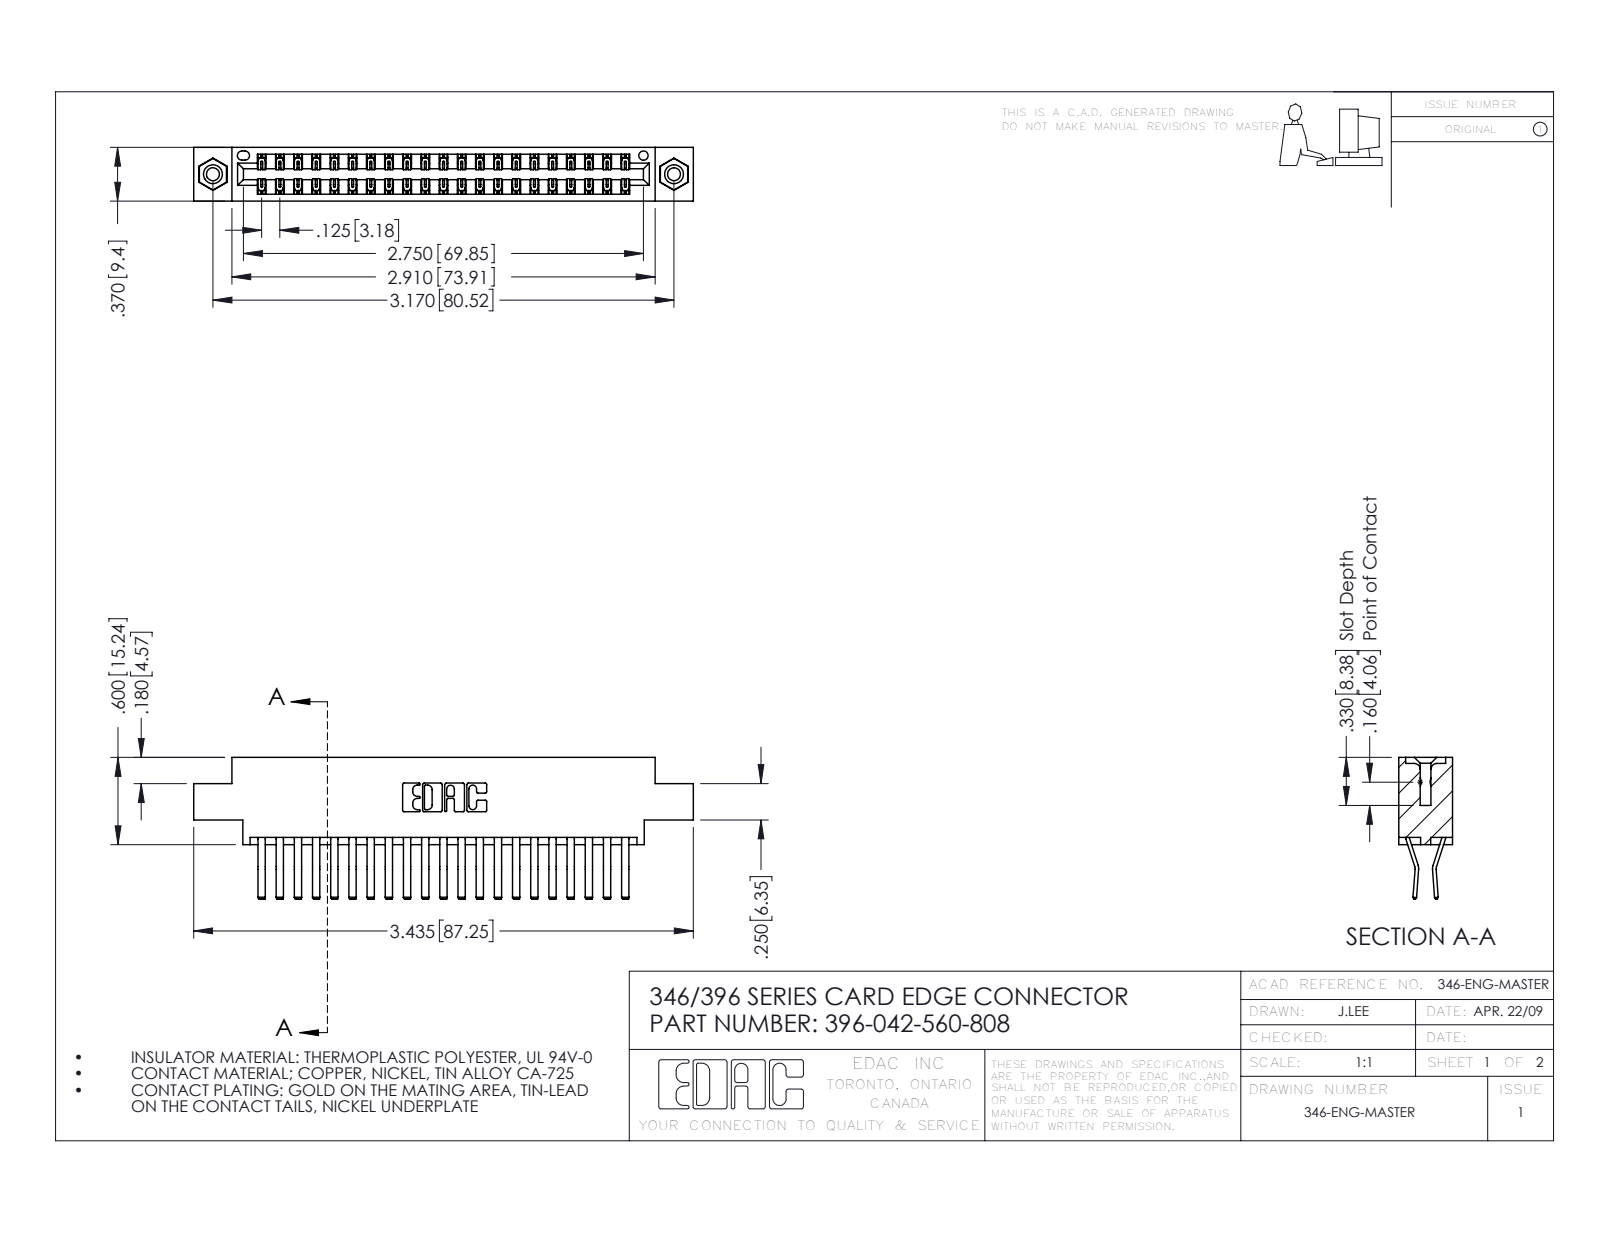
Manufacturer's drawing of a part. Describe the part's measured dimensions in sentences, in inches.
The part is named "346 Part_0.170 Offset - 0.156 Dia-TI; 345-250-001_345-250-003-102; 396-042-560-808; 345-292-001_560 Tail". Its 3-D file was written by "SolidWorks 2016 (CONFIG_CONTROL_DESIGN)". It is 45 solids with 2454 faces: 1582 planar, 856 cylindrical and 16 other. Overall it measures 3.435 by 0.975 by 0.37 inches. Its volume is 0.516 cubic inches and its surface area 18.96 square inches. Round holes: 2 of diameter 0.089, 2 of diameter 0.125, 2 of diameter 0.156, 1 of diameter 0.064. Round bosses or shafts: 2 of diameter 0.155. Partial cylindrical surfaces (rounded edges, fillets, slot ends): 63 of radius 0.006, 22 of radius 0.01, 6 of radius 0.007, 6 of radius 0.031, 3 of radius 0.026, 2 of radius 0.01, 2 of radius 0.014, 2 of radius 0.022. The main face-to-face distances are 0.048, 0.322, 0.37, 0.25, 0.025, 0.072, 0.298, 0.275, 0.222, 0.148. The hole center spacings are 0.246, 2.963, 3.17.
